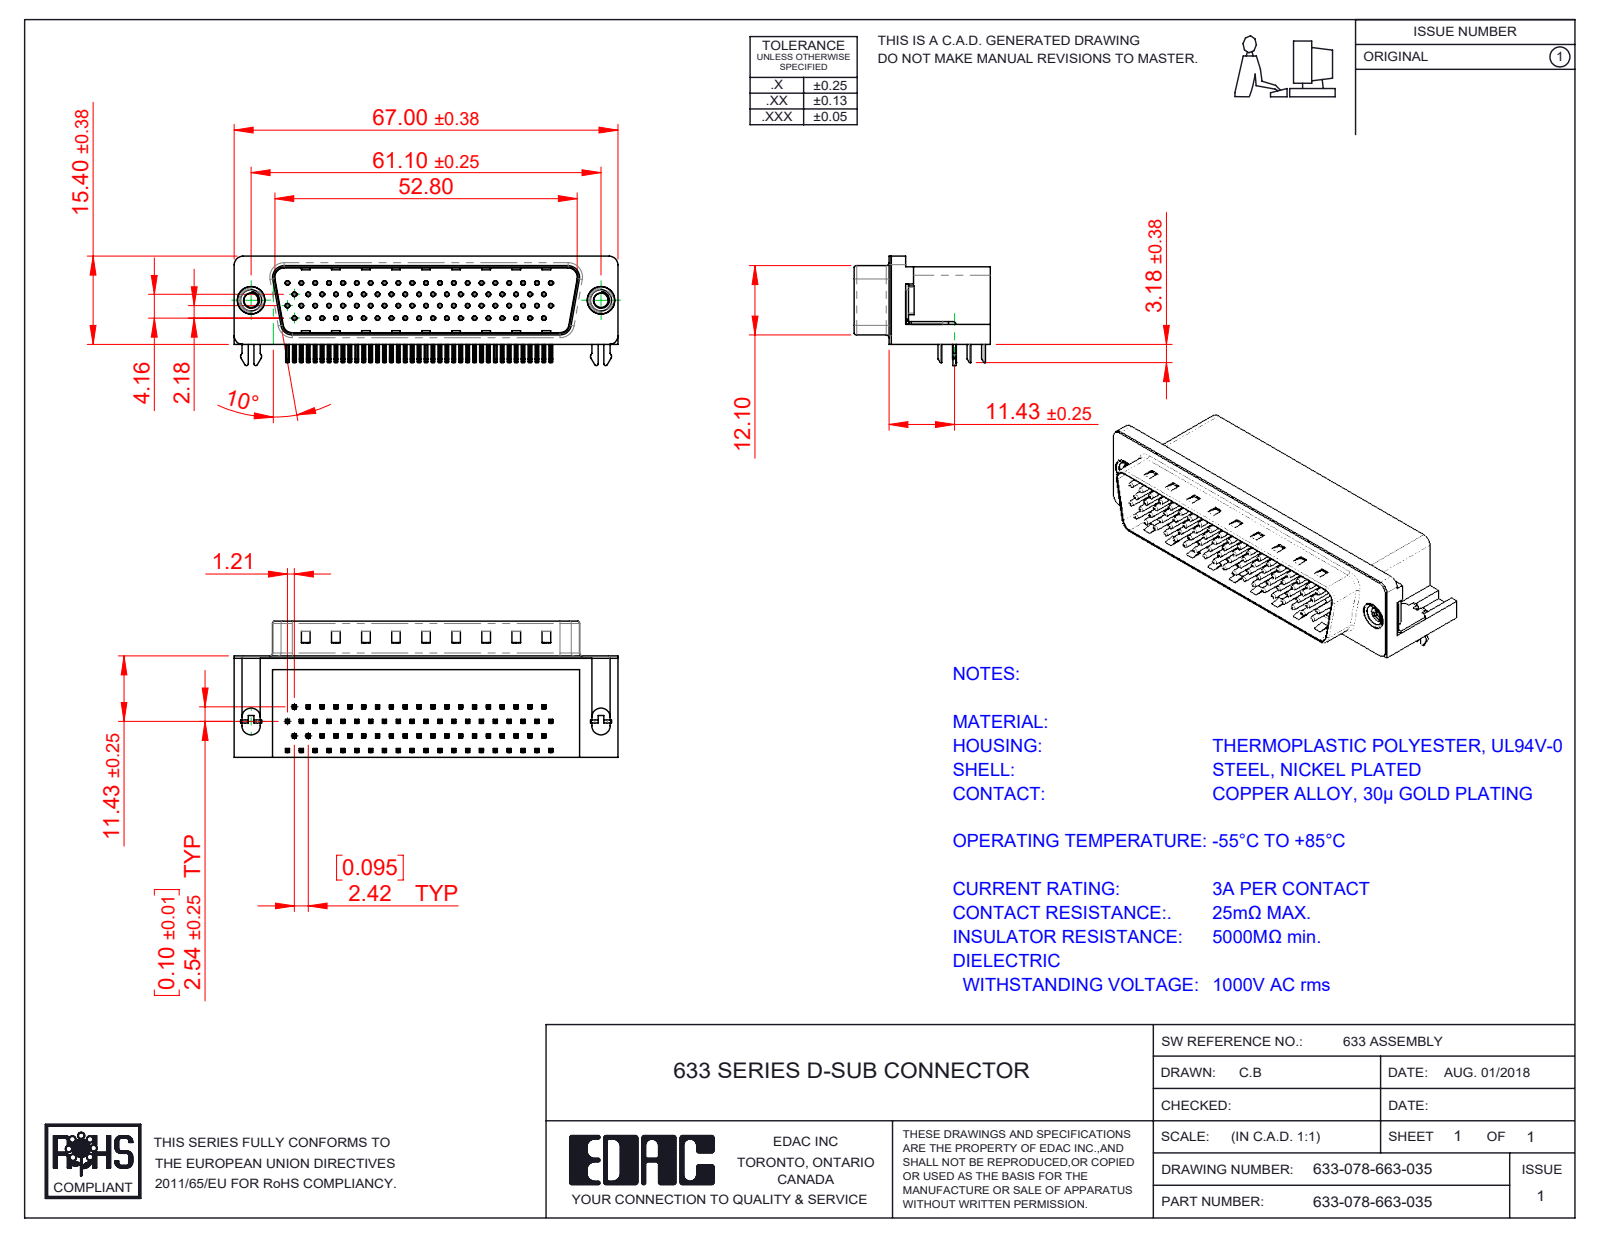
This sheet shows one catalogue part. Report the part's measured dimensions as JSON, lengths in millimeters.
{"part_name": "633 Housing_78 Contact; 633 2 Prong Board Lock_78 Contact; 633 M3 Threaded Rivet; 633 Shell_78 Contact (+5 more)", "step_written_by": "SolidWorks 2016 (CONFIG_CONTROL_DESIGN)", "units": "millimeters", "bodies": {"solids": 84, "faces": 6316, "planar": 4013, "cylindrical": 1790, "other": 513}, "overall_size": [67, 23.8, 19.1], "volume_mm3": 14607, "surface_area_mm2": 16361, "round_holes": [[0.35, 78], [0.8, 78], [2.5, 2], [4, 2], [4.8, 2], [5, 2]], "round_bosses_or_shafts": [[0.75, 78], [4.9, 2], [4.75, 2], [3.9, 2]], "partial_cylinders_radius": [[0.25, 320], [0.12, 156], [1, 16], [0.5, 14], [1.6, 8], [1.5, 6], [0.32, 4], [0.45, 4]], "face_to_face_distances": [0.4, 13.2, 17.3, 11.7, 13.35, 2.05, 13.75, 1.65, 1.85, 11.9], "hole_center_spacings": [2.42, 4.84, 7.26, 9.68, 6.26, 7.13, 12.1, 8.62]}
